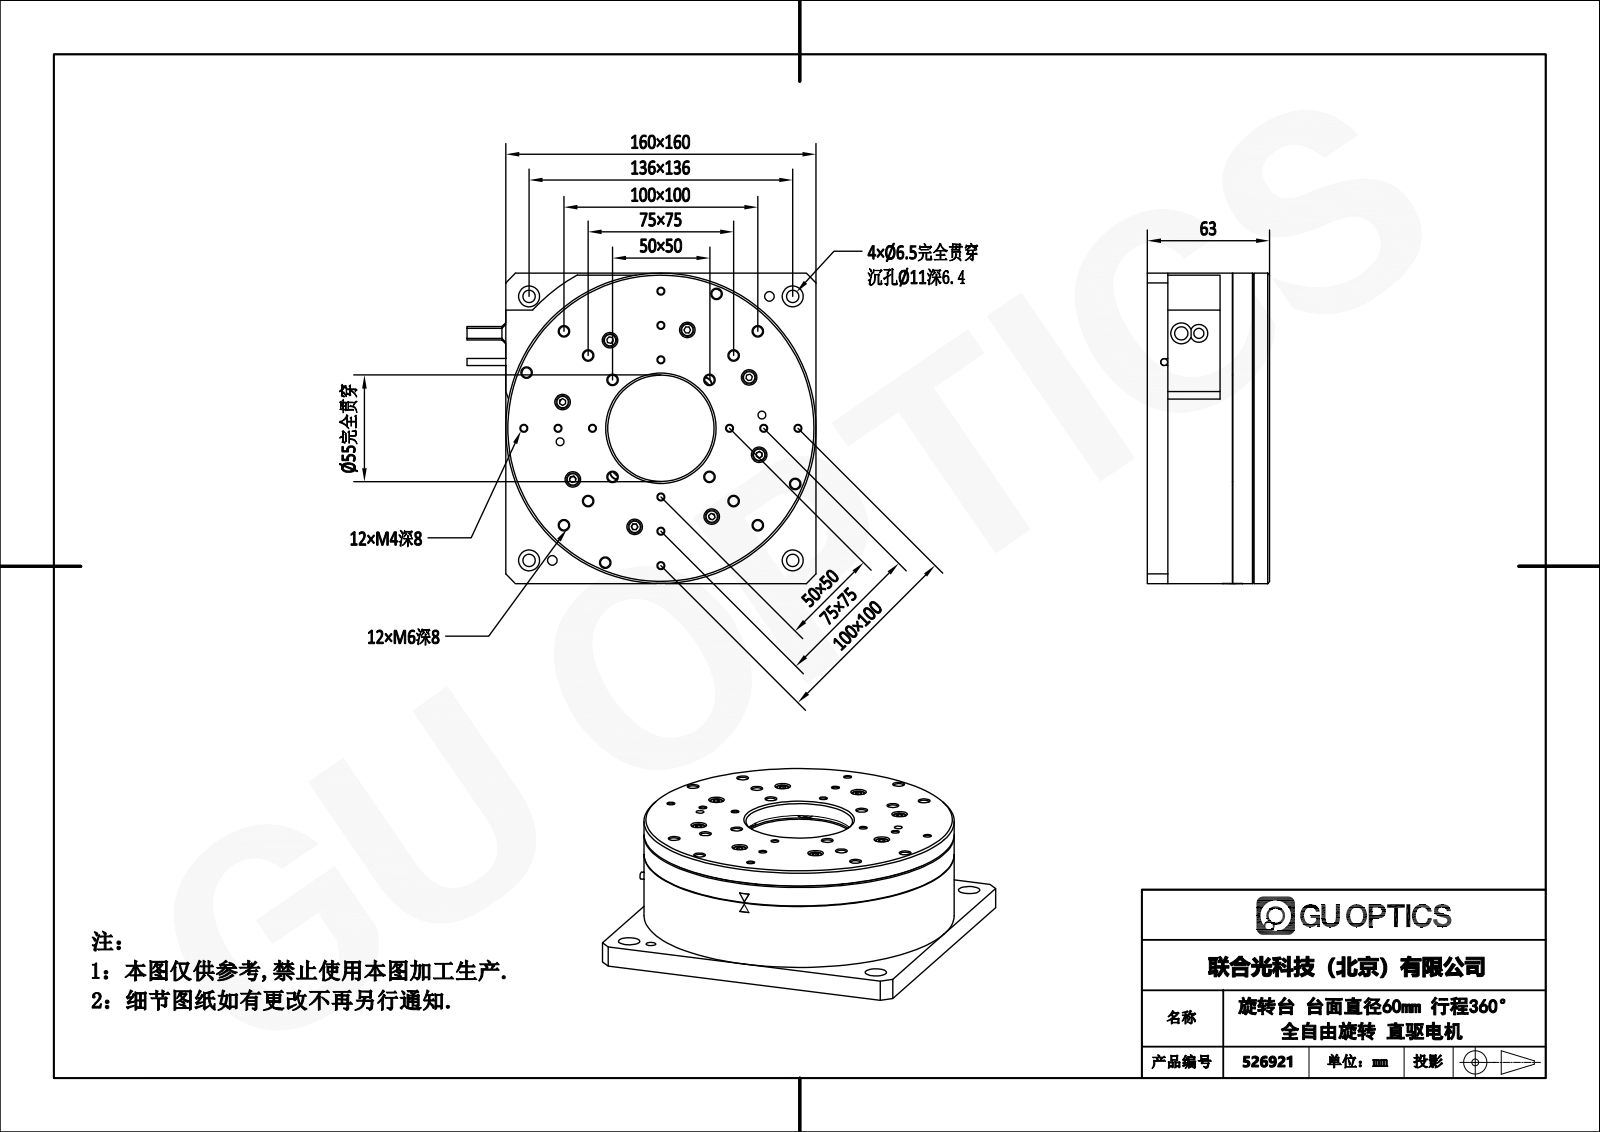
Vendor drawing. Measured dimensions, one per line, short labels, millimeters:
name: FMSR160D
written by: SolidWorks 2017 (CONFIG_CONTROL_DESIGN)
unit: mm
bodies: 0 solids, 534 faces (234 planar, 204 cylindrical, 96 other)
size: 180 × 160.05 × 63
holes: 18× ⌀5, 18× ⌀6, 12× ⌀3.3, 8× ⌀8, 4× ⌀6.5, 4× ⌀11, 2× ⌀4, 1× ⌀55, 1× ⌀55.05
bosses: 18× ⌀5.5, 7× ⌀7, 1× ⌀160, 1× ⌀5.2, 1× ⌀3.6
rounds: 1× R1.85, 1× R80.05, 1× R90
face distances: 63, 55, 8, 1, 44.5, 10.5, 52.5, 54, 43.5, 9
hole spacings: 63.5, 97.29, 125.07, 119.34, 22.06, 43.44, 81.64, 109.98
